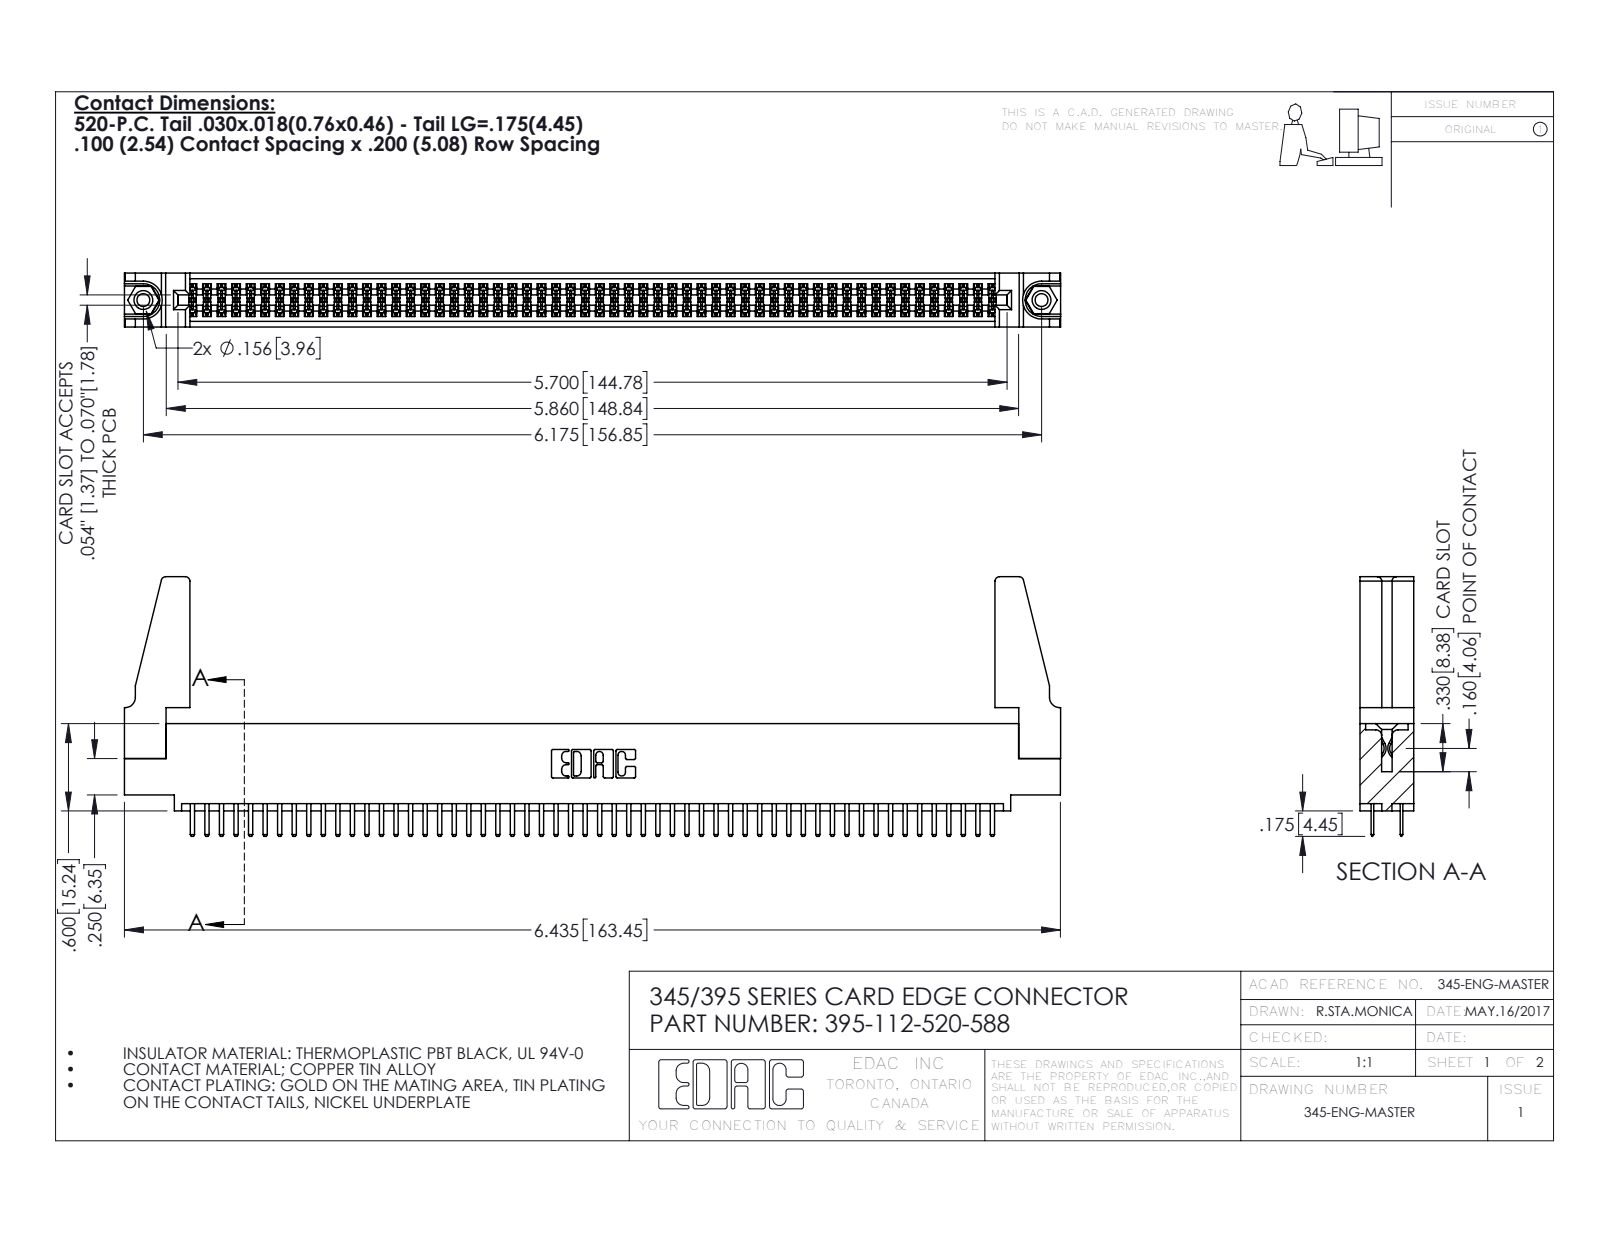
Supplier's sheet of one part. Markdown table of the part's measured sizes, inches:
| quantity | value |
| --- | --- |
| part name | 345-292-001_345-293-120; 395-112-520-588; 345-250-001_345-250-001-102; 345-220-078_345-220-088 (+1 more) |
| STEP written by | SolidWorks 2016 (CONFIG_CONTROL_DESIGN) |
| units | inches |
| bodies | 117 solids, 6302 faces (4076 planar, 2210 cylindrical, 16 other) |
| overall size | 6.436 × 1.785 × 0.37 |
| volume | 1.168 in³ |
| surface area | 41.64 in² |
| round holes (diameter × count) | 0.089 × 2, 0.125 × 2, 0.156 × 2, 0.064 × 1 |
| round bosses / shafts (diameter × count) | 0.155 × 2 |
| partial cylindrical surfaces (radius × count) | 0.006 × 168, 0.01 × 116, 0.01 × 22, 0.03 × 8, 0.007 × 6, 0.031 × 6, 0.026 × 3, 0.014 × 2 |
| main face-to-face distances | 0.072, 0.298, 0.37, 0.2, 0.098, 0.272, 0.025, 0.225, 0.022, 0.072 |
| hole center spacings | 0.27, 5.939, 6.175 |
